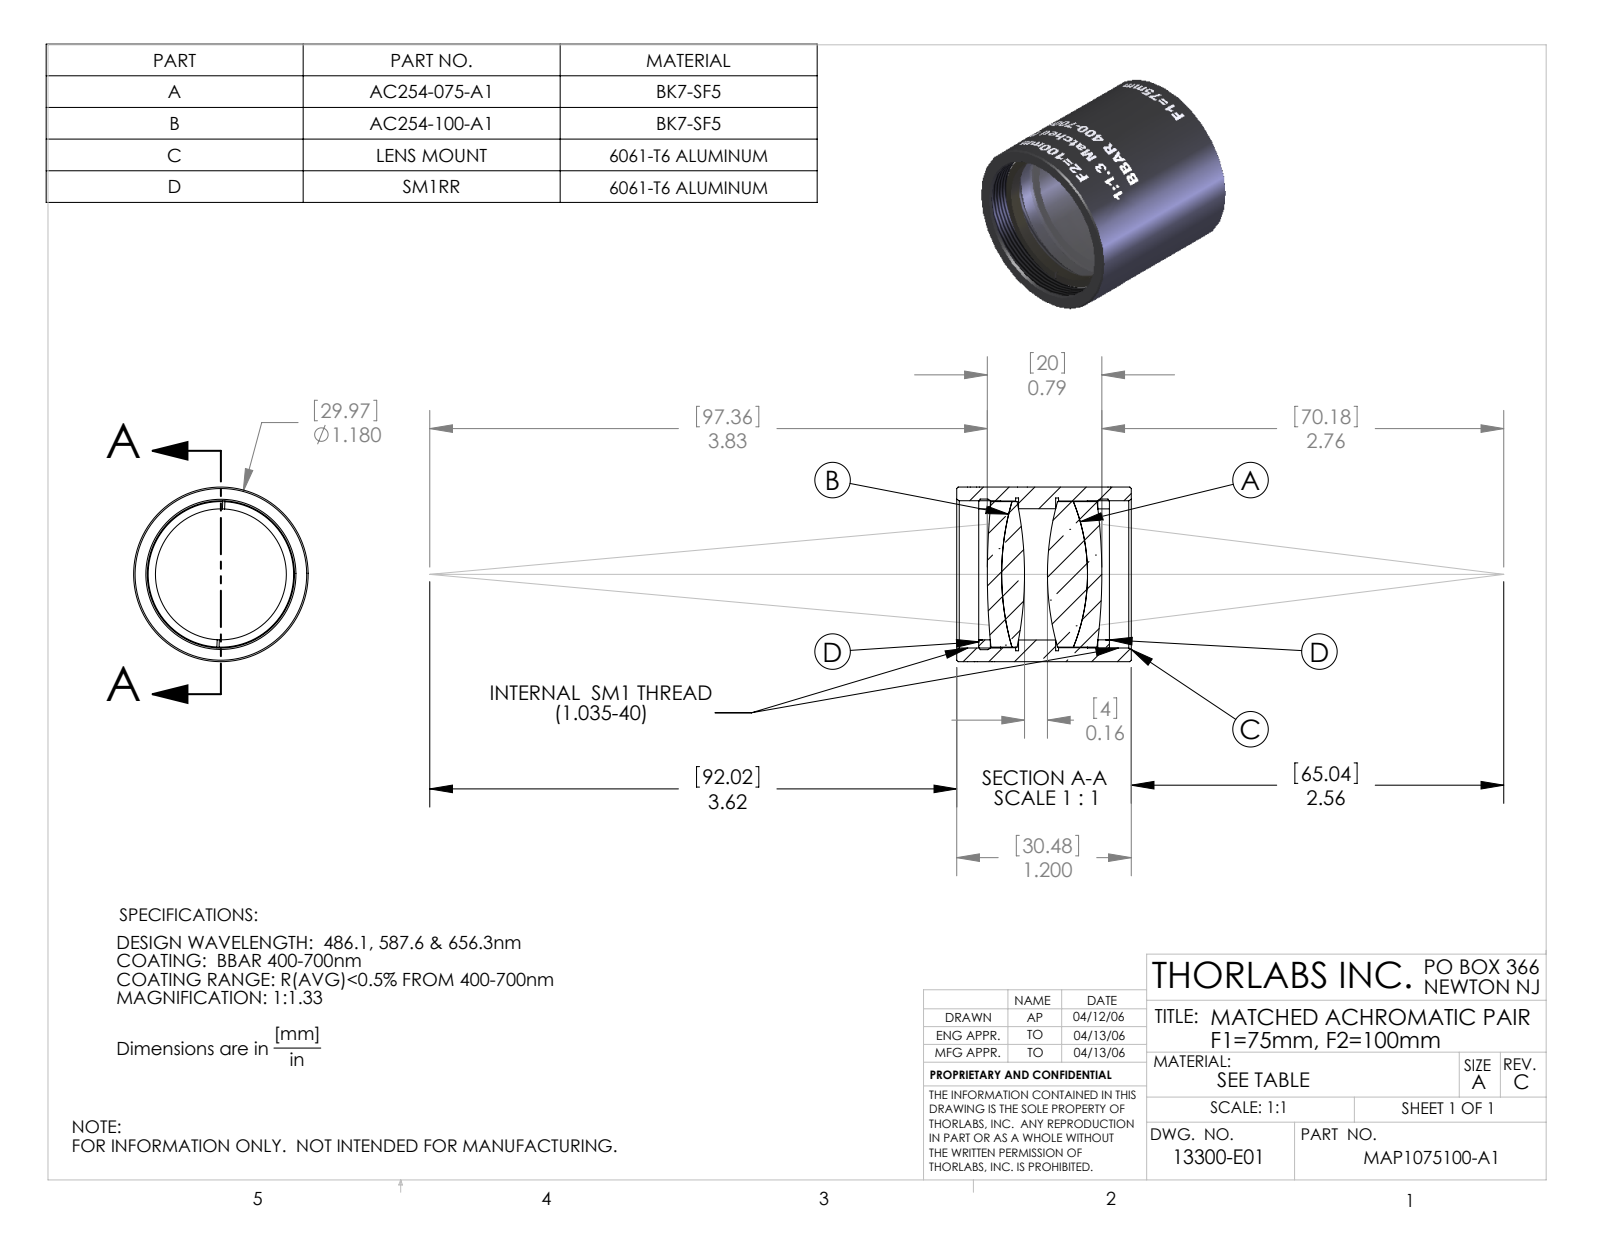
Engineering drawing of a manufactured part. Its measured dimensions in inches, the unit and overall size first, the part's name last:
Units: inches
Overall size (bounding box): 1.2 × 1.2 × 1.2
Round holes (diameter × count): ⌀0.9 ×1, ⌀1.012 ×1
Round bosses / shafts (diameter × count): ⌀1.2 ×1
Main face-to-face distances: 1.2, 0.15, 1.05, 1.049, 0.898, 0.151, 0.015, 0.025, 0.874, 0.175
Bodies: 0 solids, 145 faces (18 planar, 111 cylindrical, 16 other)
Part name (STEP PRODUCT): 13300-E0W
STEP written by: SolidWorks 2007 (AUTOMOTIVE_DESIGN)
